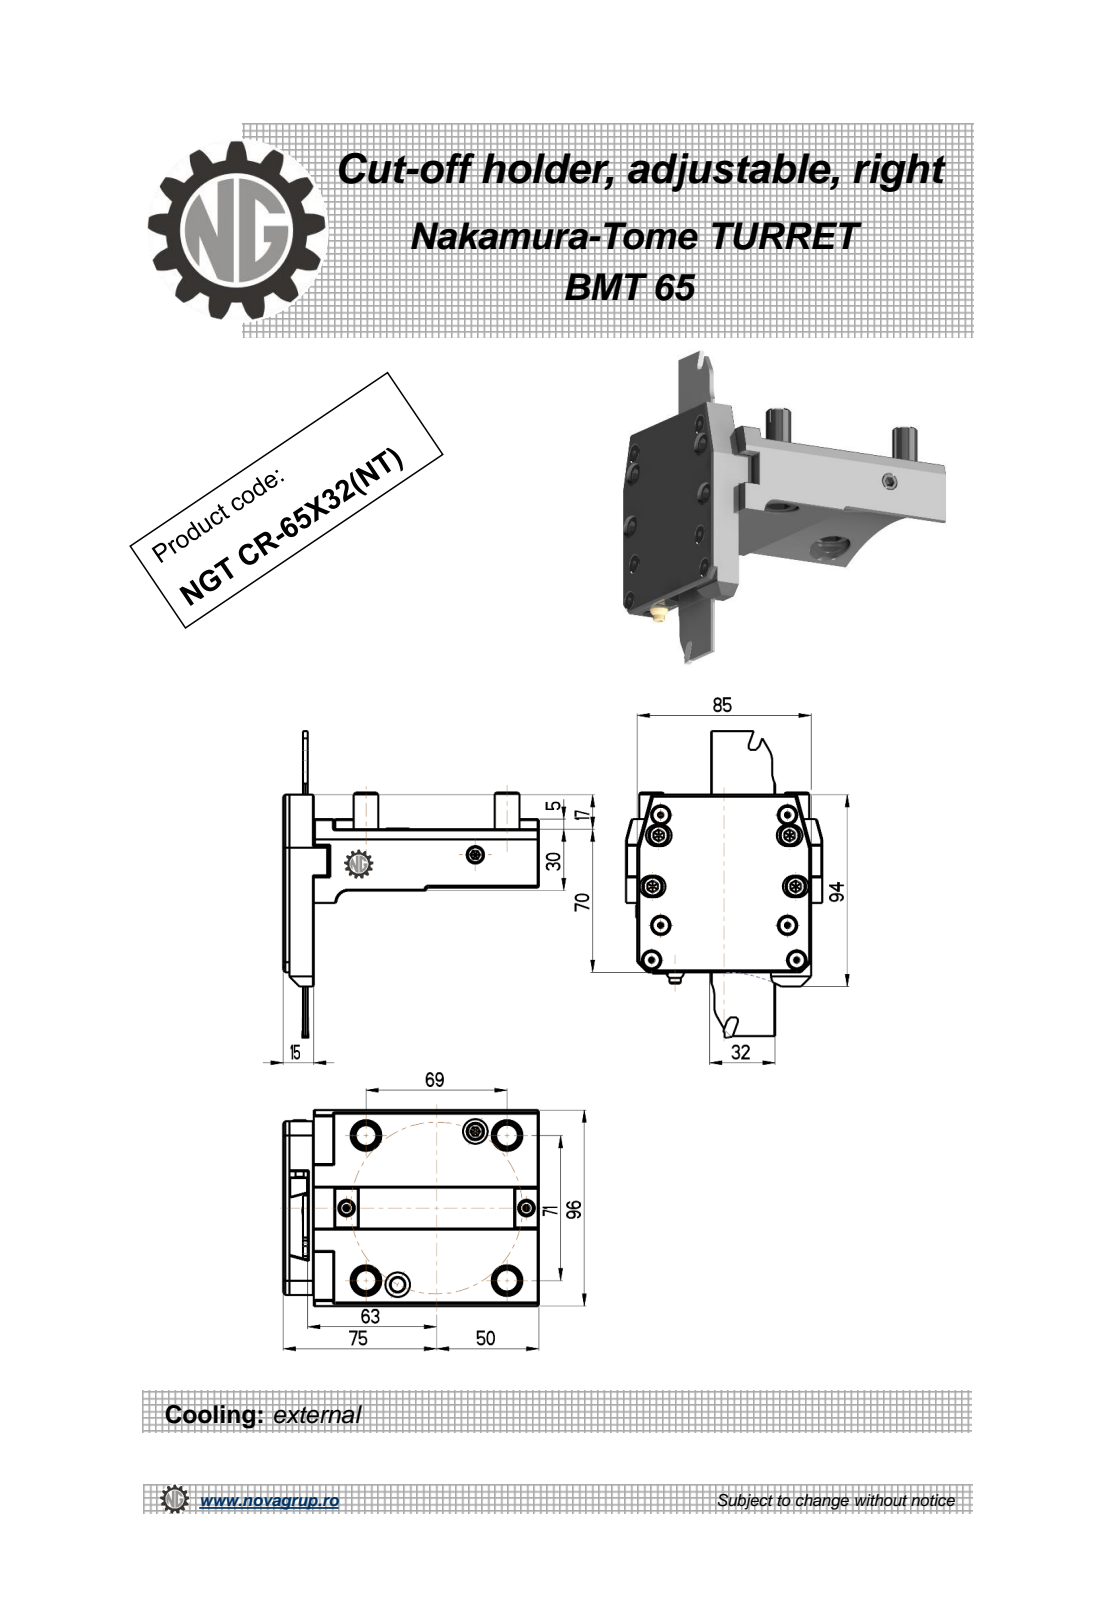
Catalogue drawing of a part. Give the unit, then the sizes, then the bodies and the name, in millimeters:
Units: millimetres
Overall size (bounding box): 125 × 96 × 95
Round holes (diameter × count): ⌀5 ×2, ⌀8 ×2, ⌀12 ×2, ⌀3.5 ×1, ⌀6.8 ×1
Round bosses / shafts (diameter × count): ⌀12 ×4, ⌀10 ×4, ⌀4 ×3, ⌀8 ×1, ⌀7 ×1, ⌀5.5 ×1
Partial cylindrical surfaces — rounded edges, fillets, slot ends (radius × count): R0.2 ×24, R0.31 ×12, R5.25 ×8, R0.14 ×6, R0.16 ×6, R0.41 ×6, R1 ×1, R6 ×1
Main face-to-face distances: 12, 3, 15, 30, 9, 5, 25, 96, 22, 110
Hole centre spacings: 41.5, 77.1, 84.08, 85.57
Volume: 352 750 mm³ · Surface area: 68 732 mm²
Bodies: 1 solid, 486 faces (290 planar, 116 cylindrical, 80 other)
Part name (STEP PRODUCT): NGT_CR_65_32_NT
STEP written by: PRO/ENGINEER BY PARAMETRIC TECHNOLOGY CORPORATION, 2010280 (CONFIG_CONTROL_DESIGN)
